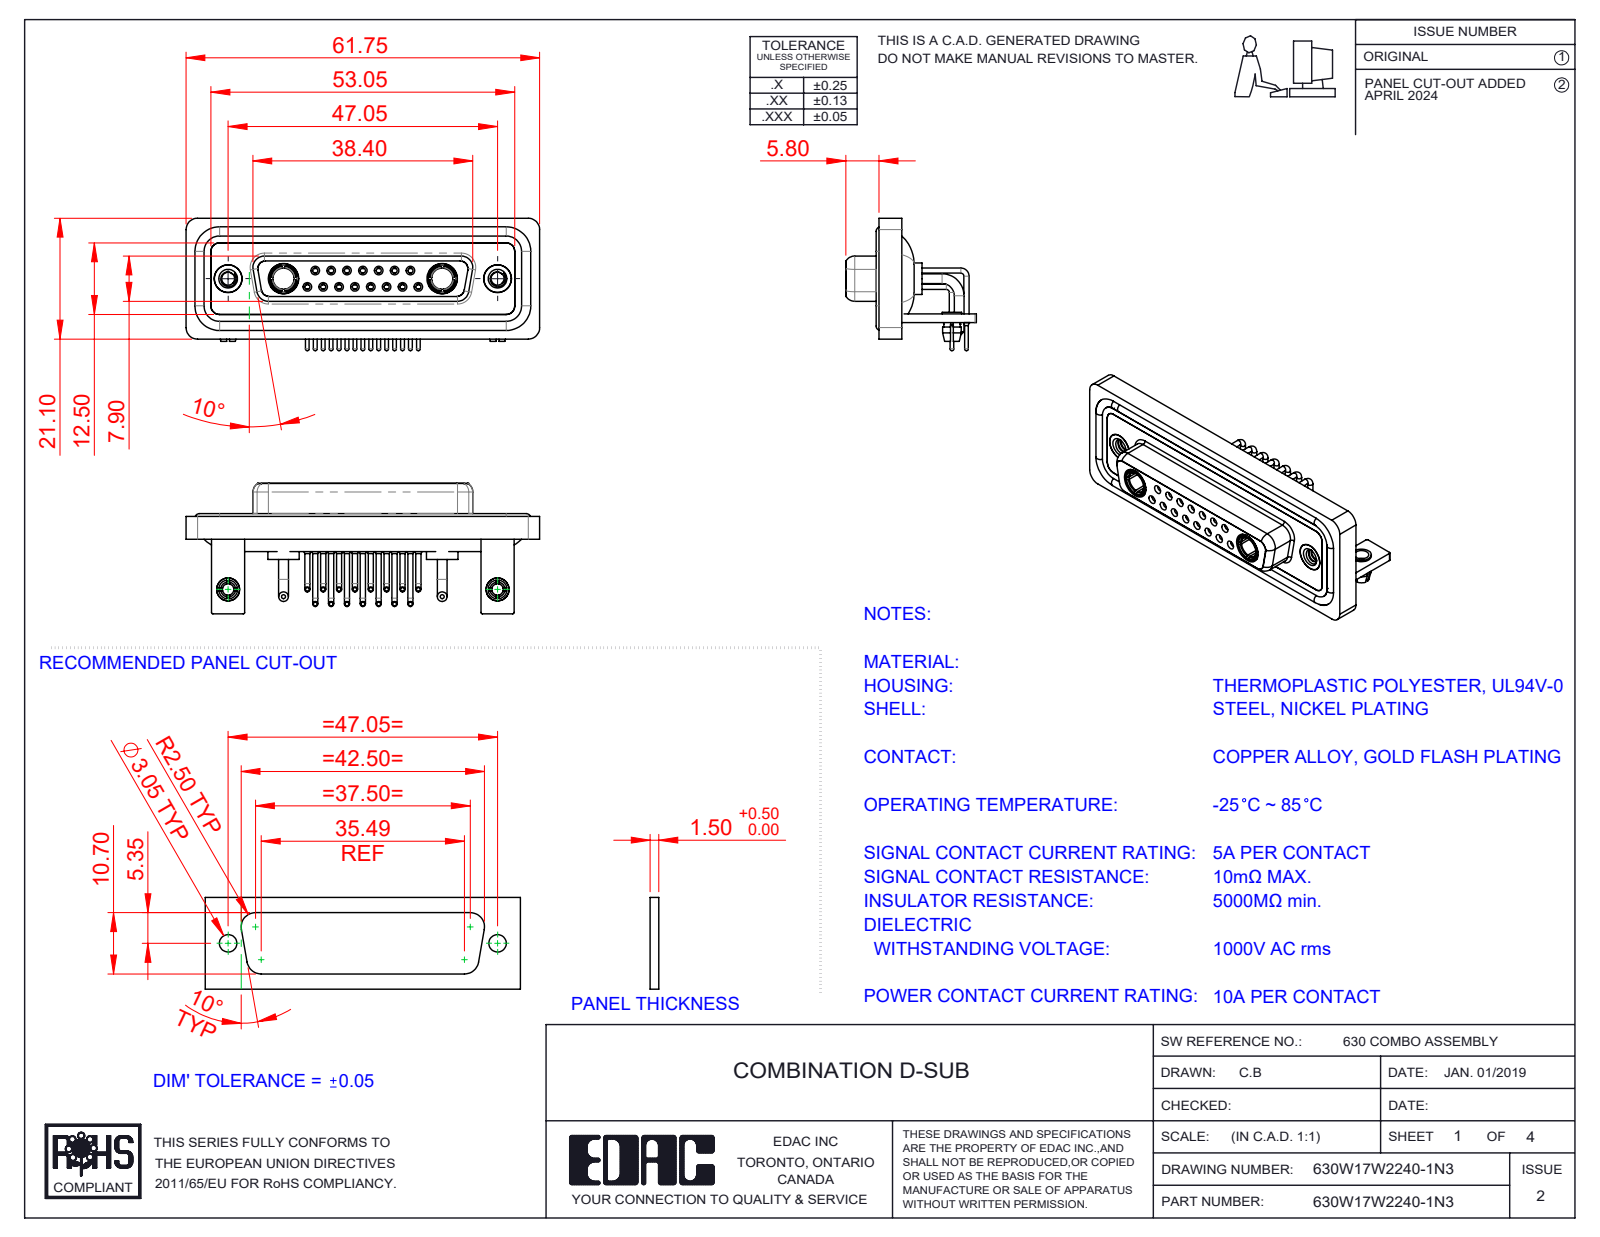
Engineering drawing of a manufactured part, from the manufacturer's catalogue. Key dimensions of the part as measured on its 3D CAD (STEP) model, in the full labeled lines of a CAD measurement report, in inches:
Part name (STEP PRODUCT): 630Combo Contact Row 2_50 Contacts; 630Combo Stabilizer Bracket_50 Contacts; 630Combo Contact Row 1_50 Contacts; 630Combo Shell Rear_25 Contacts (+7 more)
STEP written by: SolidWorks 2023 (CONFIG_CONTROL_DESIGN)
Units: inches
Bodies: 30 solids, 1477 faces (456 planar, 639 cylindrical, 382 other)
Overall size (bounding box): 2.431 × 0.91 × 0.898
Volume: 0.535 in³ · Surface area: 23.83 in²
Round holes (diameter × count): ⌀0.079 ×17, ⌀0.035 ×15, ⌀0.043 ×15, ⌀0.059 ×15, ⌀0.063 ×8, ⌀0.067 ×7, ⌀0.191 ×4, ⌀0.089 ×2, ⌀0.098 ×2, ⌀0.126 ×2, ⌀0.146 ×2, ⌀0.157 ×2
Round bosses / shafts (diameter × count): ⌀0.035 ×15, ⌀0.026 ×15, ⌀0.063 ×11, ⌀0.067 ×4, ⌀0.217 ×2, ⌀0.205 ×2, ⌀0.195 ×2, ⌀0.195 ×2
Partial cylindrical surfaces — rounded edges, fillets, slot ends (radius × count): R0.079 ×19, R0.059 ×18, R0.01 ×16, R0.053 ×8, R0.063 ×8, R0.02 ×5, R0.024 ×4, R0.026 ×4
Main face-to-face distances: 0.016, 0.071, 0.114, 0.059, 0.146, 0.161, 0.043, 0.055, 0.063, 0.122
Hole centre spacings: 0.124, 0.109, 0.218, 0.327, 0.198, 0.295, 0.436, 0.198
